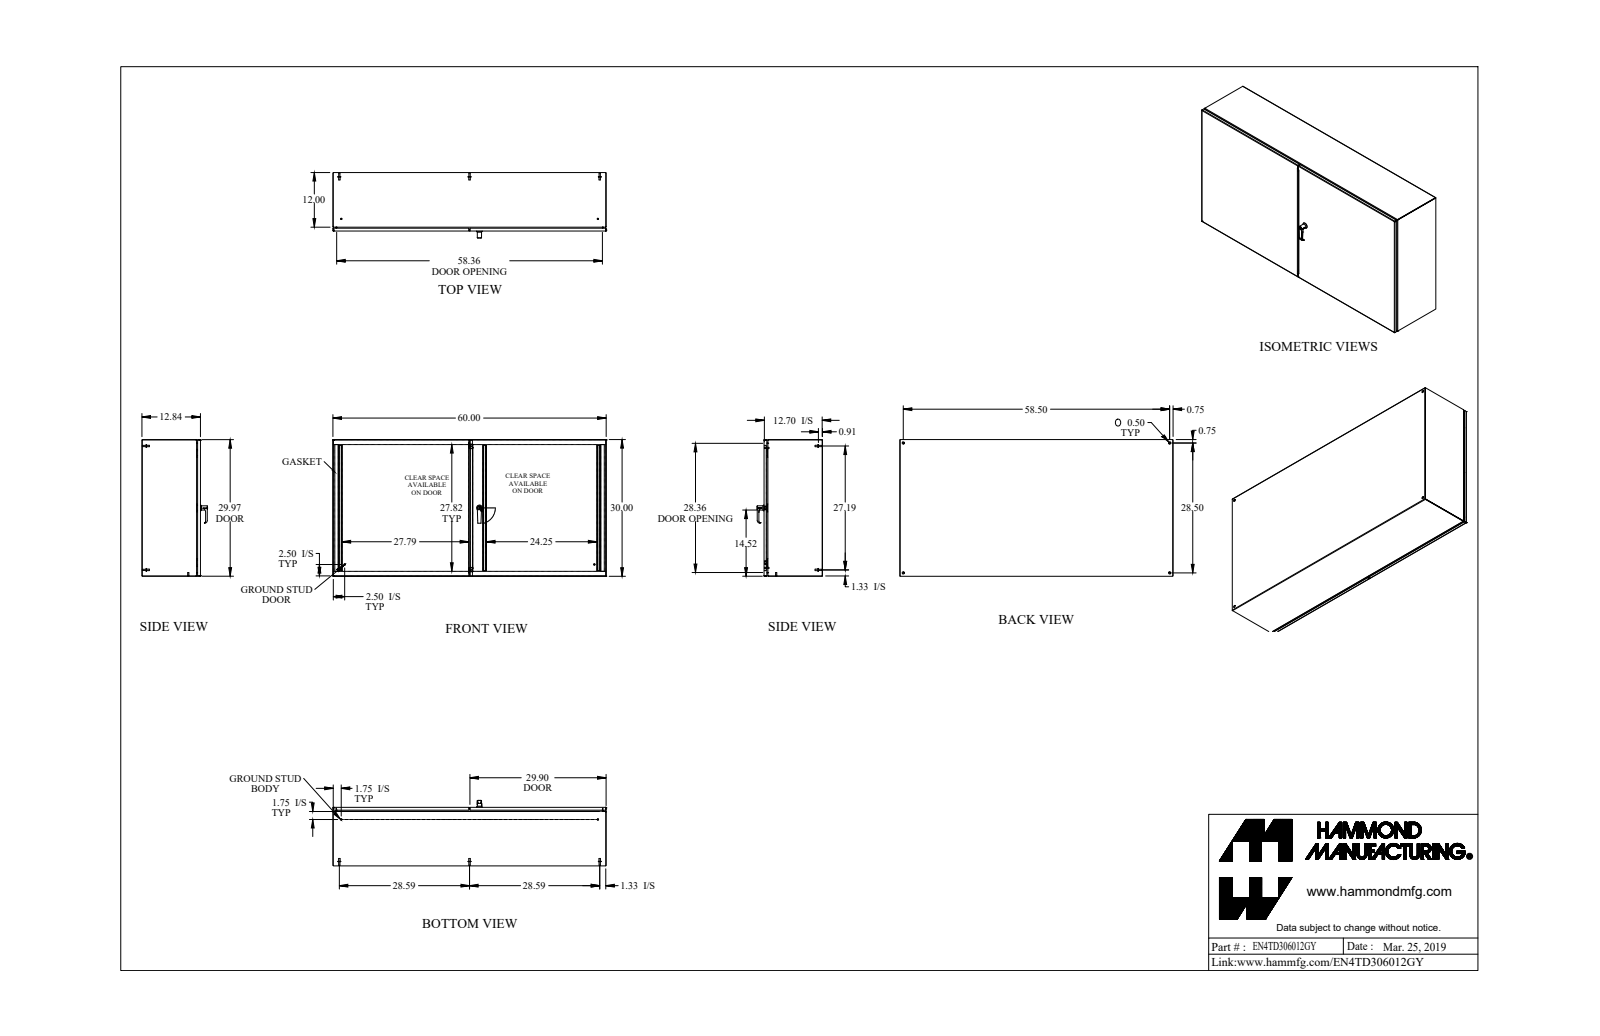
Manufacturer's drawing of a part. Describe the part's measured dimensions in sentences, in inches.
The part is named "EN4TD306012GY". Its 3-D file was written by "SolidWorks 2018 (AUTOMOTIVE_DESIGN)". It is 91 solids with 2297 faces: 1053 planar, 846 cylindrical and 398 other. Overall it measures 60 by 30 by 14.372 inches. Its volume is 510.1 cubic inches and its surface area 13 647 square inches. Round holes: 5 of diameter 0.196, 4 of diameter 0.176, 4 of diameter 0.265, 4 of diameter 0.5, 3 of diameter 0.24, 3 of diameter 0.242, 2 of diameter 0.172, 2 of diameter 0.25, 2 of diameter 0.256, 2 of diameter 0.26, 2 of diameter 0.275, 2 of diameter 0.313. Round bosses or shafts: 10 of diameter 0.25, 8 of diameter 0.625, 6 of diameter 0.313, 6 of diameter 0.27, 4 of diameter 0.51, 4 of diameter 0.375, 4 of diameter 0.281, 4 of diameter 0.156. Partial cylindrical surfaces (rounded edges, fillets, slot ends): 30 of radius 0.043, 30 of radius 0.081, 26 of radius 0.036, 26 of radius 0.108, 25 of radius 0.063, 20 of radius 0.094, 16 of radius 0.02, 15 of radius 0.016. The main face-to-face distances are 0.072, 12.77, 12.698, 12.842, 29.928, 29.856, 59.928, 30, 59.856, 60. The hole center spacings are 0.786, 13.188, 26.792, 28.5, 30.603, 31.748, 34.498, 58.5.
